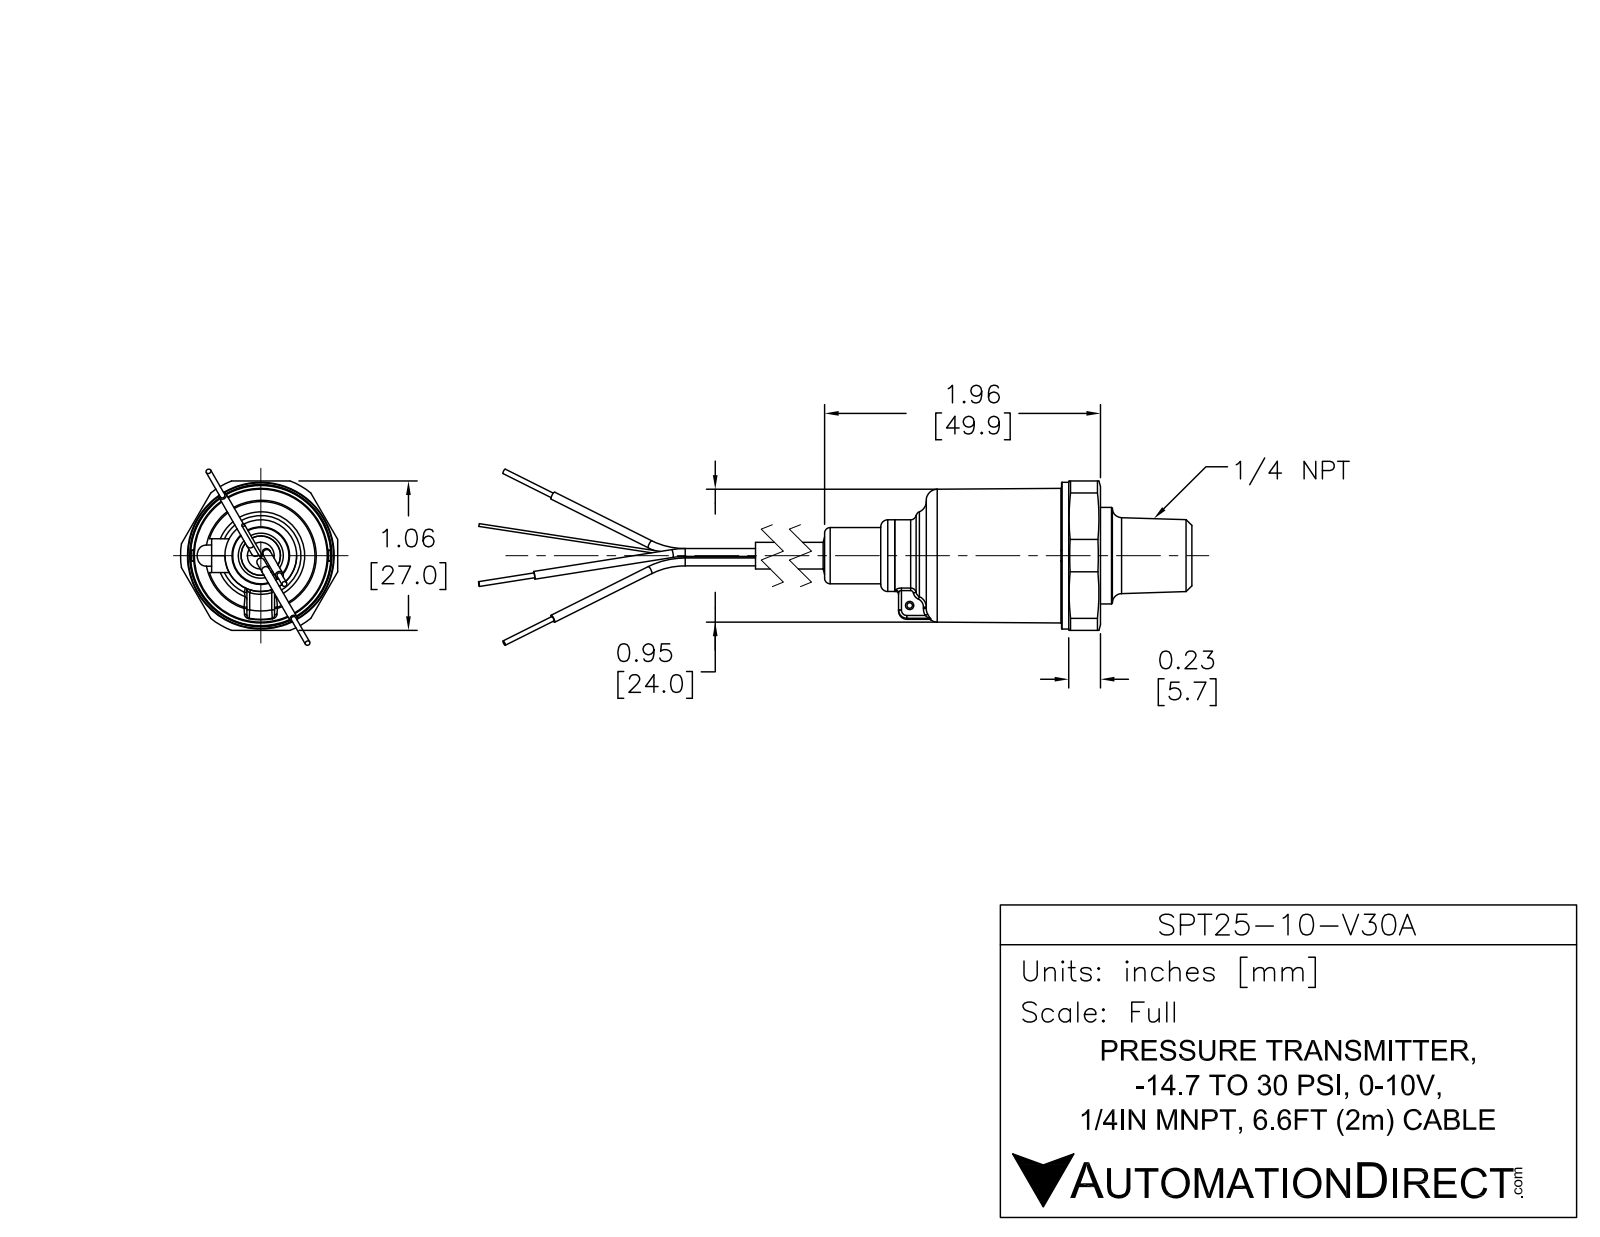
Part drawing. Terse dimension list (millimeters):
name: SPT25-10-V30A
written by: SolidWorks 2011 (AUTOMOTIVE_DESIGN)
unit: mm
bodies: 7 solids, 75 faces (32 planar, 27 cylindrical, 16 other)
size: 153.3 × 29 × 27.09
volume: 20 801 mm³; area: 7 170 mm²
holes: 1× ⌀1, 1× ⌀3.3
bosses: 6× ⌀1.4, 5× ⌀0.75, 1× ⌀26.75, 1× ⌀24, 1× ⌀17.5, 1× ⌀14, 1× ⌀13, 1× ⌀10
rounds: 1× R2, 1× R14.5
face distances: 6.75, 24, 17.25, 42.75, 49.5, 66.75, 44, 1.25, 5.5, 22.75
